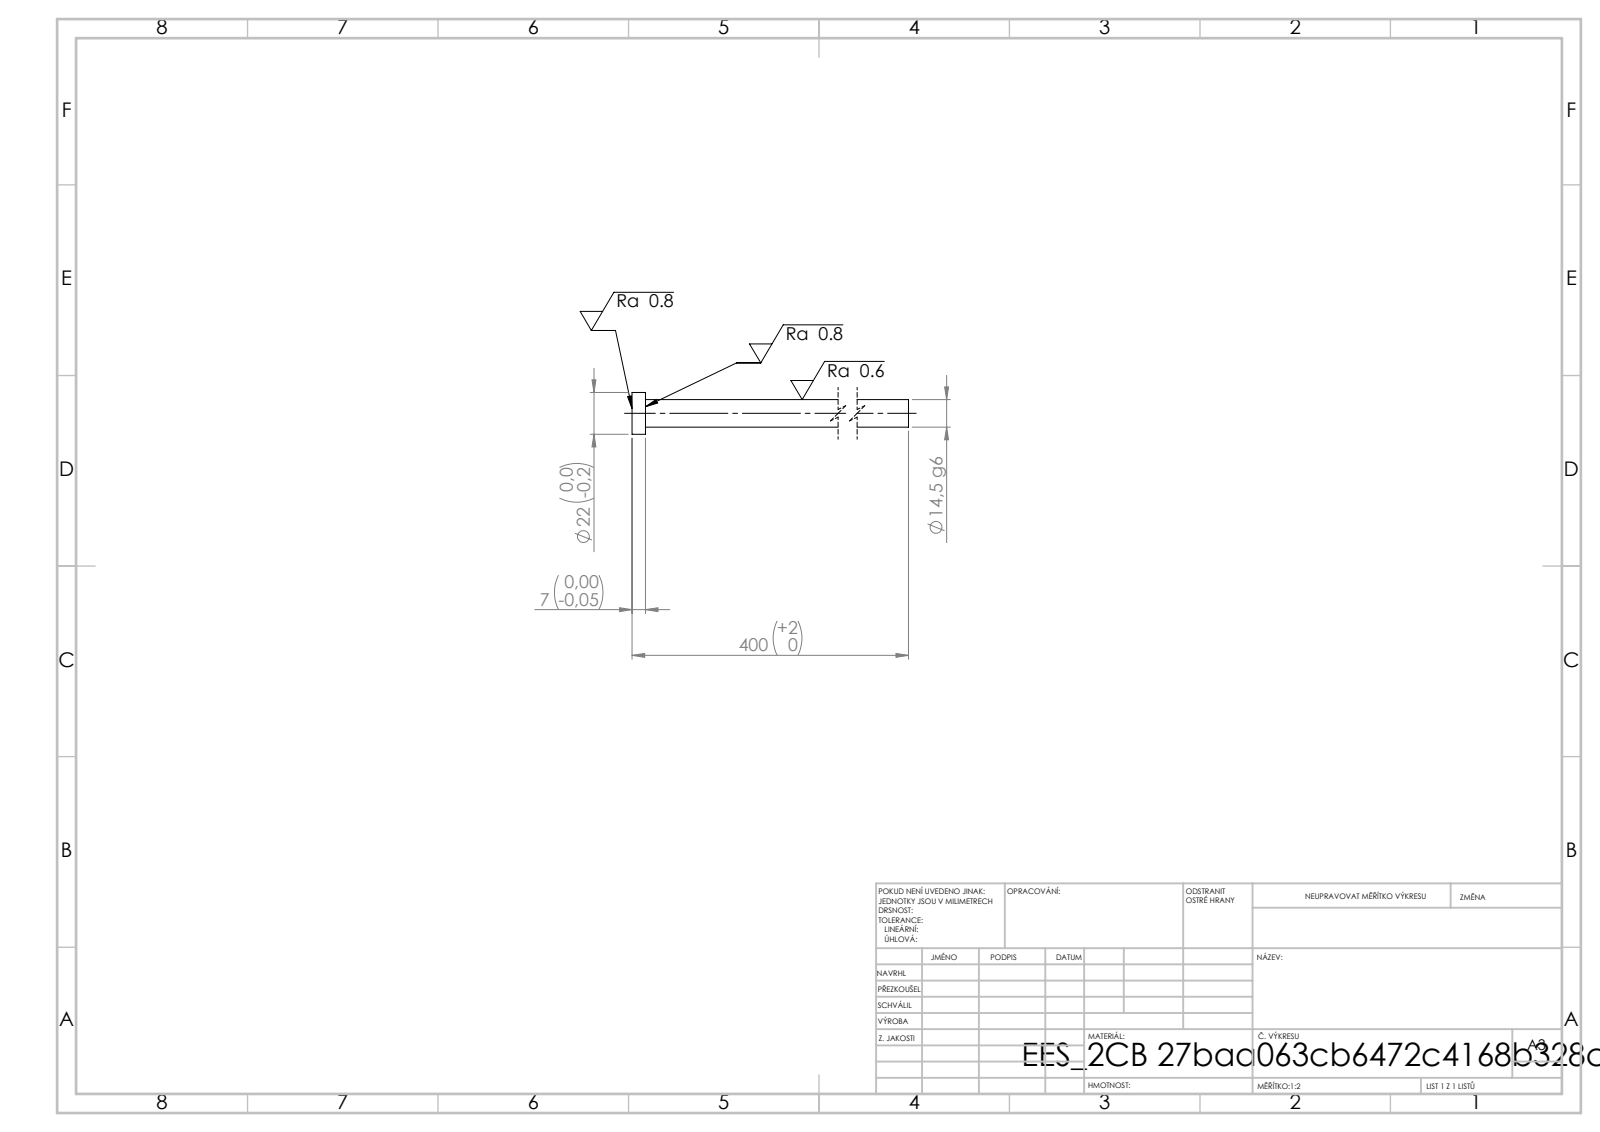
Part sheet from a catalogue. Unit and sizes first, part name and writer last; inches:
Units: inches
Overall size (bounding box): 15.748 × 0.866 × 0.866
Round bosses / shafts (diameter × count): ⌀0.866 ×1, ⌀0.571 ×1
Main face-to-face distances: 0.276, 15.748, 15.472
Volume: 4.123 in³ · Surface area: 29.68 in²
Bodies: 1 solid, 7 faces (3 planar, 4 cylindrical, 0 other)
STEP written by: SolidWorks 2019 (CONFIG_CONTROL_DESIGN)
